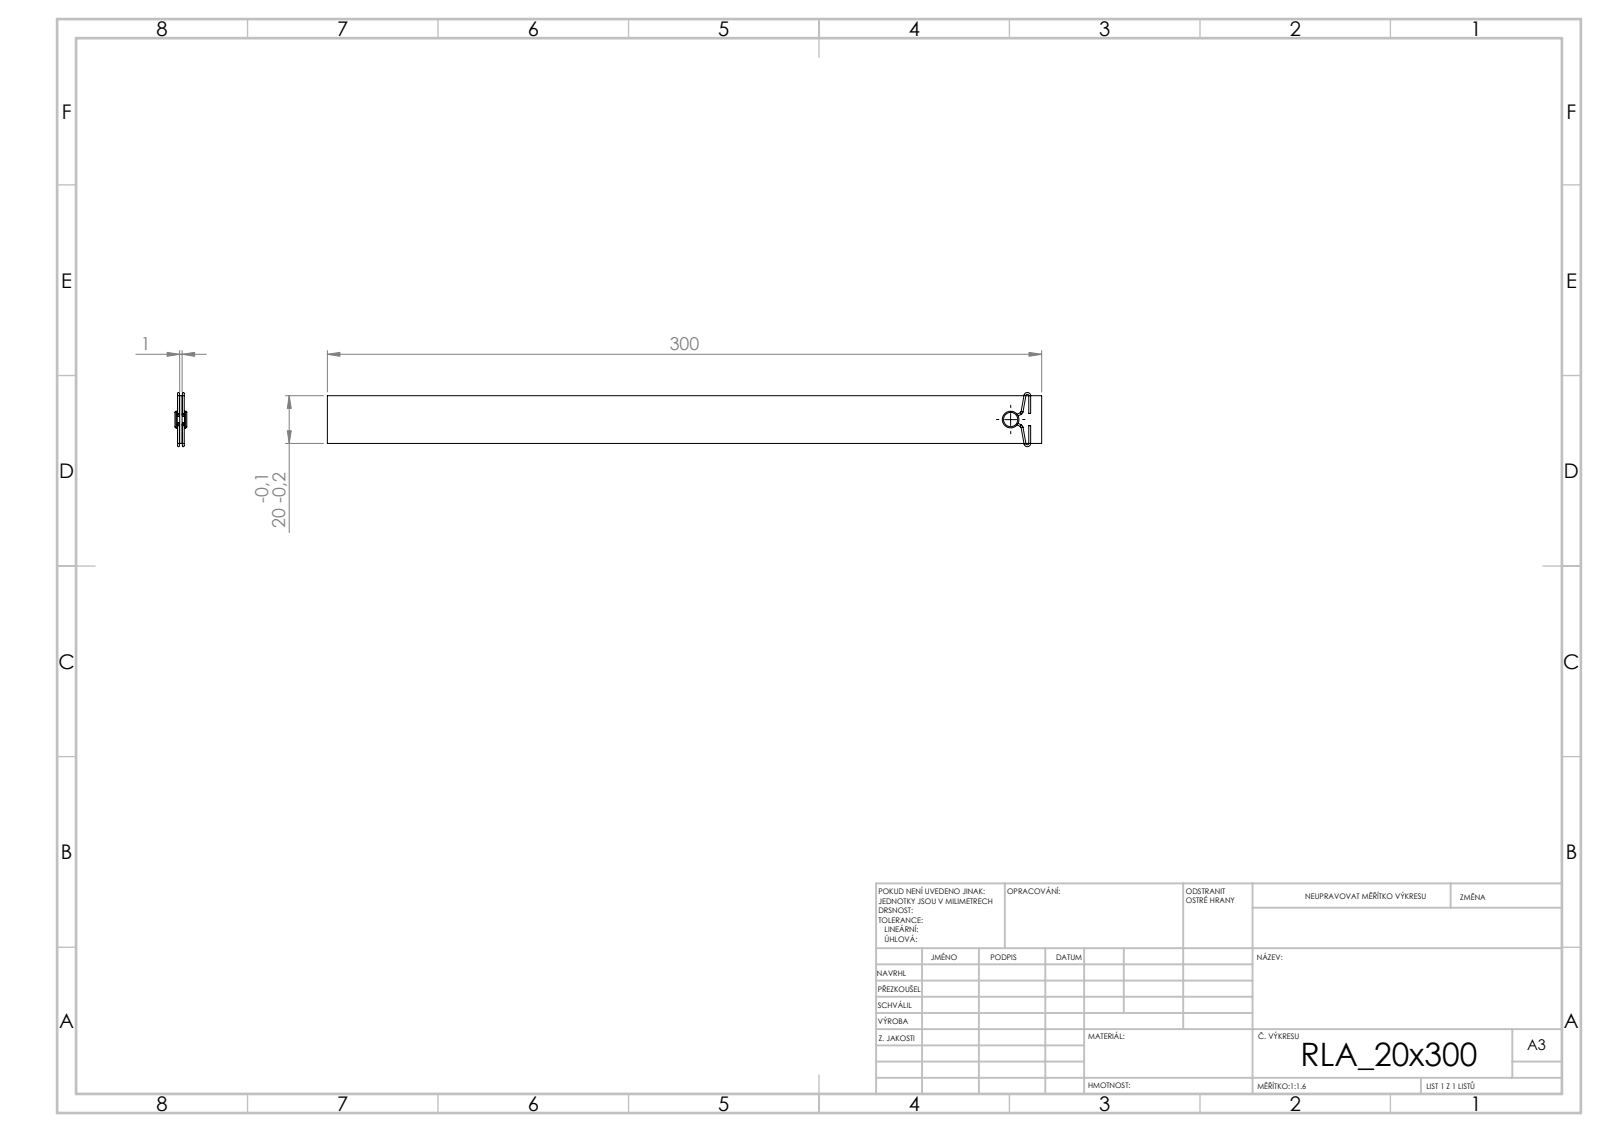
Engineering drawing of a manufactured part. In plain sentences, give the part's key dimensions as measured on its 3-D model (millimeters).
Its 3-D file was written by "SolidWorks 2019 (CONFIG_CONTROL_DESIGN)". It is 3 solids with 82 faces: 14 planar, 40 cylindrical and 28 other. Overall it measures 300 by 22.8 by 5 millimeters. Its volume is 6 154 cubic millimeters and its surface area 13 075 square millimeters. Round bosses or shafts: 14 of diameter 0.8, 1 of diameter 7, 1 of diameter 4. The main face-to-face distances are 1, 20, 2, 3, 4, 5, 300, 7.45, 12.55, 5.1.
